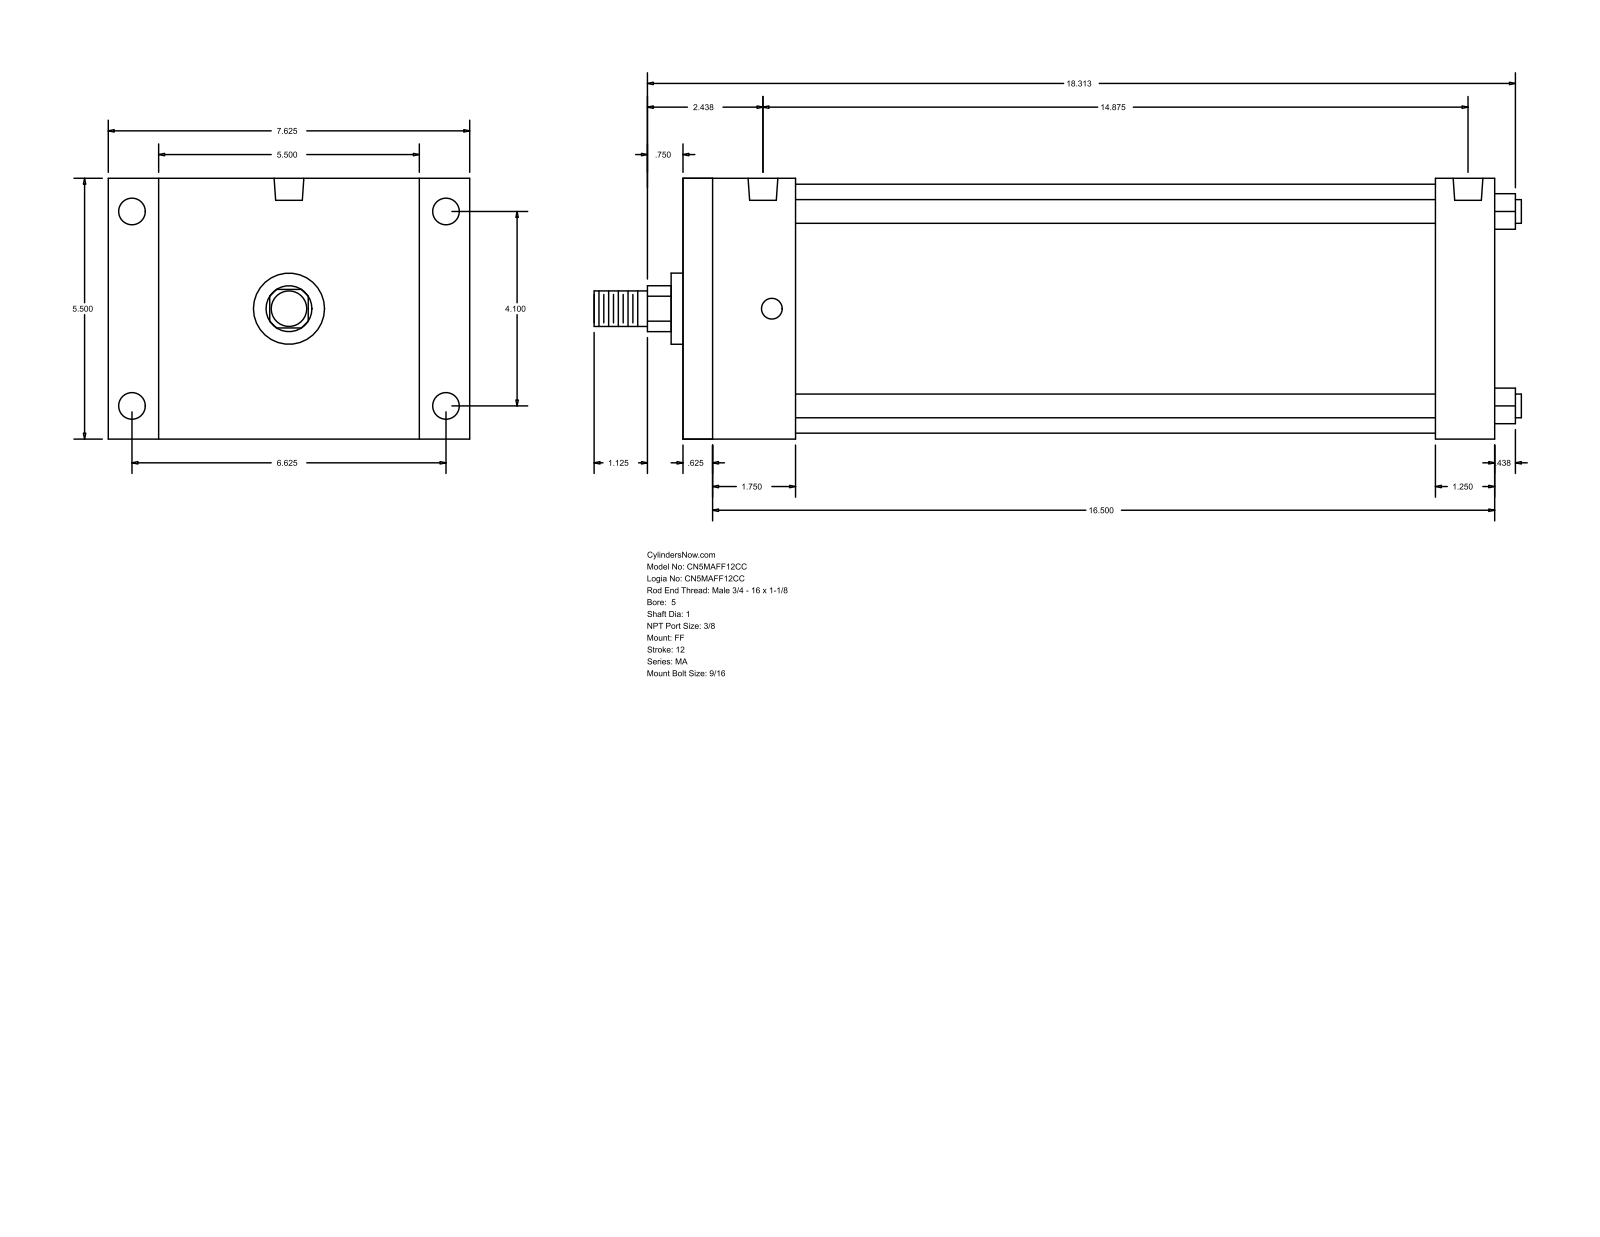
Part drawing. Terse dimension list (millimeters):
name: MA_FF__0500_1
written by: GSSL Pune (CONFIG_CONTROL_DESIGN)
unit: mm
bodies: 0 solids, 92 faces (64 planar, 28 cylindrical, 0 other)
size: 496.89 × 193.68 × 139.7
holes: 4× ⌀11.11, 4× ⌀14.29, 2× ⌀15.93
bosses: 4× ⌀12.7, 1× ⌀133.35, 1× ⌀38.1, 1× ⌀25.4, 1× ⌀19.05
rounds: 1× R12.29
face distances: 139.7, 434.97, 15.87, 419.1, 403.22, 387.35, 31.75, 60.33, 44.46, 342.89
hole spacings: 4.76, 104.14, 168.28, 197.9, 368.31, 373.07, 377.83
